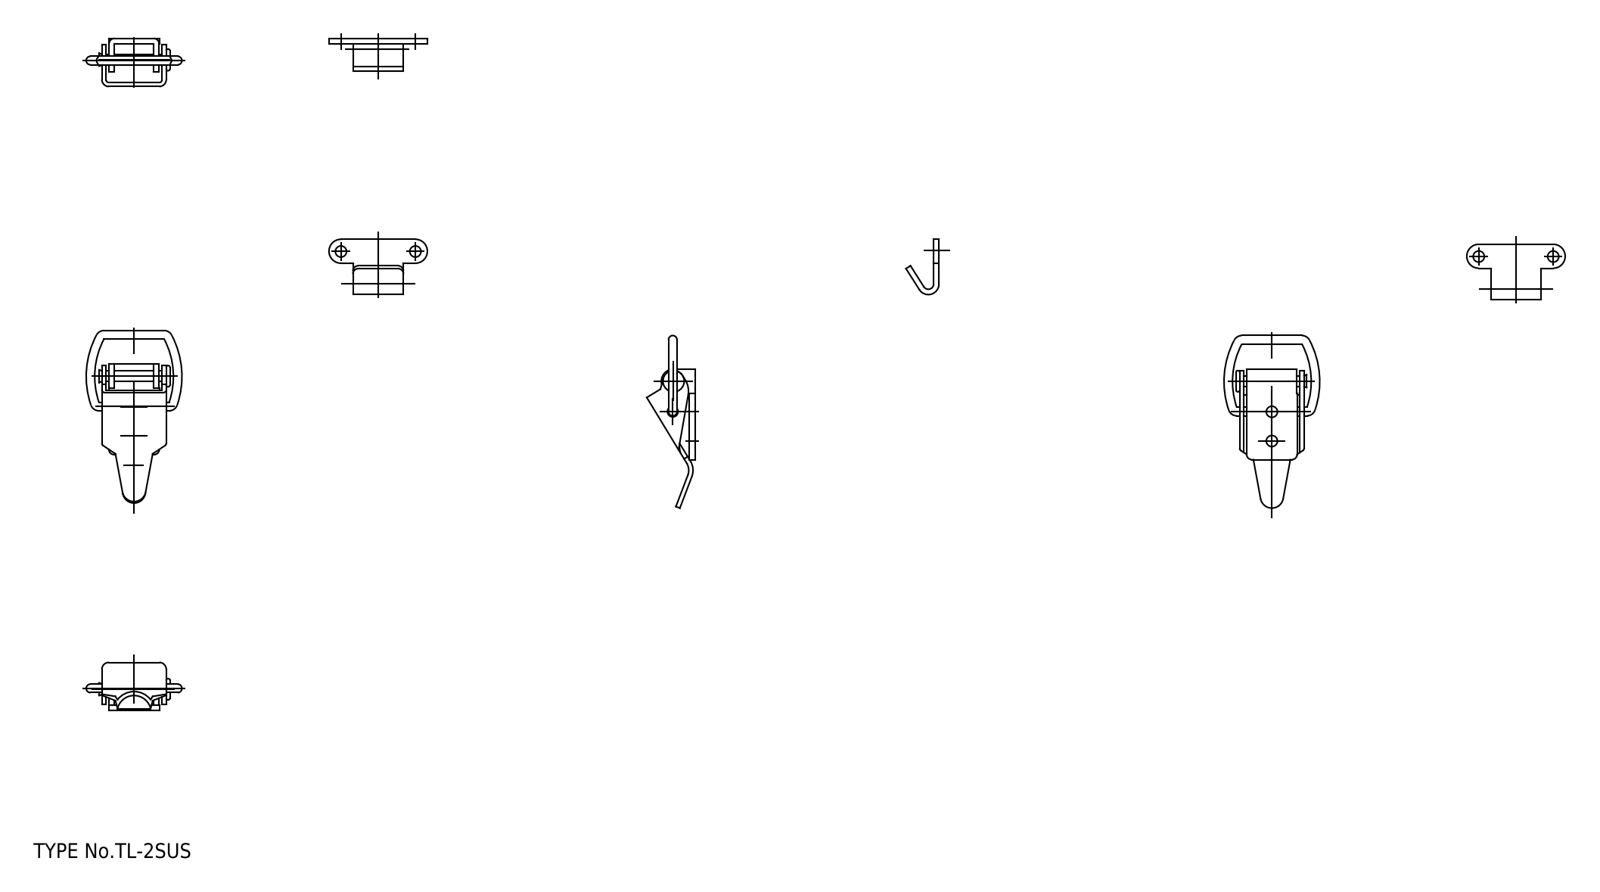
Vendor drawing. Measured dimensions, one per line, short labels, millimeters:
name: アーム; キーパー; ベース; レバー
written by: spGate 19.8.4 (****-****-****-****) (AUTOMOTIVE_DESIGN)
unit: mm
bodies: 4 solids, 115 faces (49 planar, 56 cylindrical, 10 other)
size: 39.9 × 18.5 × 9.04
volume: 754 mm³; area: 1 950 mm²
holes: 5× ⌀2.1, 1× ⌀2, 1× ⌀2.2
bosses: 2× ⌀1.6, 1× ⌀2
rounds: 7× R1, 5× R2.25, 4× R1.6, 2× R0.5, 2× R1.3, 2× R2, 1× R2.5, 1× R3.3
face distances: 1, 0.81, 0.8, 11.3, 10.5, 12.1, 8.5, 1.25, 0.45, 10.05
hole spacings: 20.71, 25.95, 5.5, 5.71, 14
